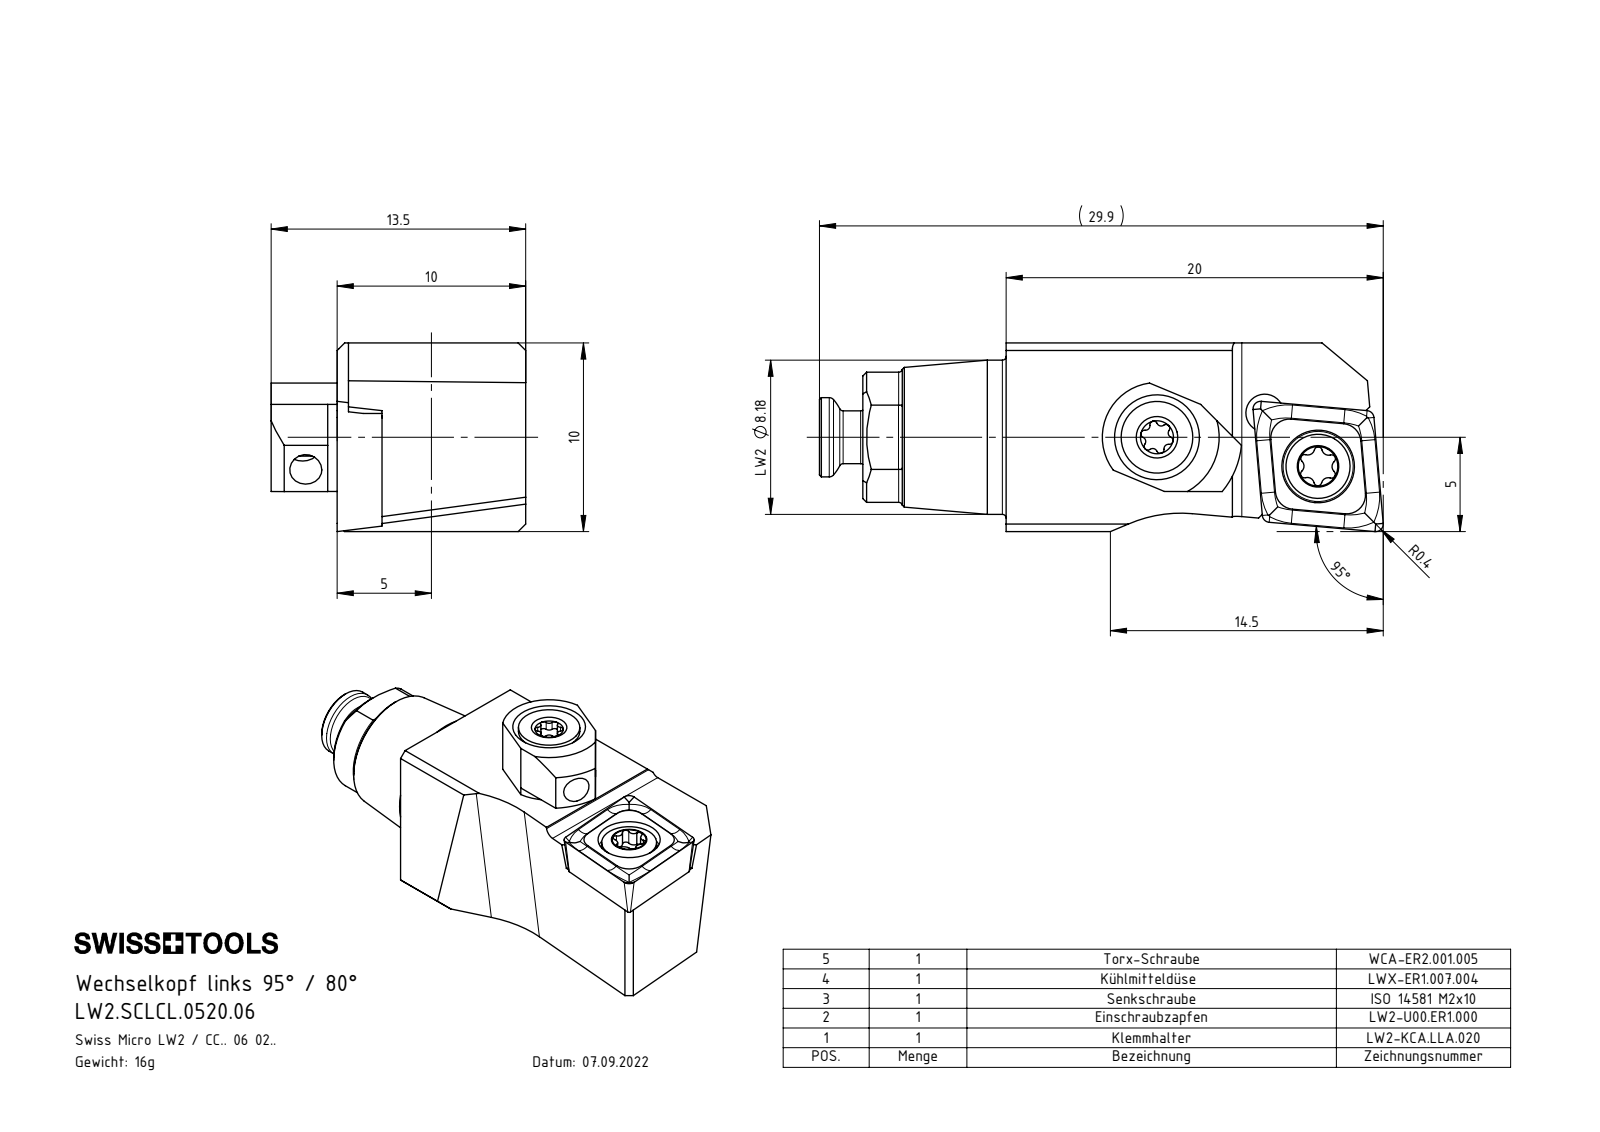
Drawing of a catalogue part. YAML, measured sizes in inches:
part_name: "LW2-U00.ER1.000_A; LW2-KCA.LLA.020_A; ISO 14581 - M2x10; CCMT060204 (+3 more)"
step_written_by: "SolidWorks 2022 (CONFIG_CONTROL_DESIGN)"
units: inches
bodies: {solids: 6, faces: 261, planar: 63, cylindrical: 96, other: 102}
overall_size: [1.177, 0.472, 0.394]
volume: 0.122
surface_area: 2.761
round_holes:
  - {diameter: 0.039, count: 1}
  - {diameter: 0.059, count: 1}
  - {diameter: 0.063, count: 1}
  - {diameter: 0.079, count: 1}
  - {diameter: 0.081, count: 1}
  - {diameter: 0.11, count: 1}
  - {diameter: 0.118, count: 1}
  - {diameter: 0.138, count: 1}
  - {diameter: 0.152, count: 1}
round_bosses_or_shafts:
  - {diameter: 0.322, count: 1}
  - {diameter: 0.165, count: 1}
  - {diameter: 0.157, count: 1}
  - {diameter: 0.15, count: 1}
  - {diameter: 0.134, count: 1}
  - {diameter: 0.118, count: 1}
  - {diameter: 0.11, count: 1}
  - {diameter: 0.098, count: 1}
partial_cylinders:
  - {radius: 0.008, count: 8}
  - {radius: 0.007, count: 6}
  - {radius: 0.008, count: 6}
  - {radius: 0.009, count: 6}
  - {radius: 0.011, count: 6}
  - {radius: 0.014, count: 5}
  - {radius: 0.014, count: 1}
  - {radius: 0.02, count: 1}
face_to_face_distances: [0.394, 0.3, 0.094, 0.37, 0.07, 0.024, 0.299, 0.043, 0.079, 0.315]
hole_center_spacings: [0.157, 0.158, 0.23, 0.342, 0.342]
